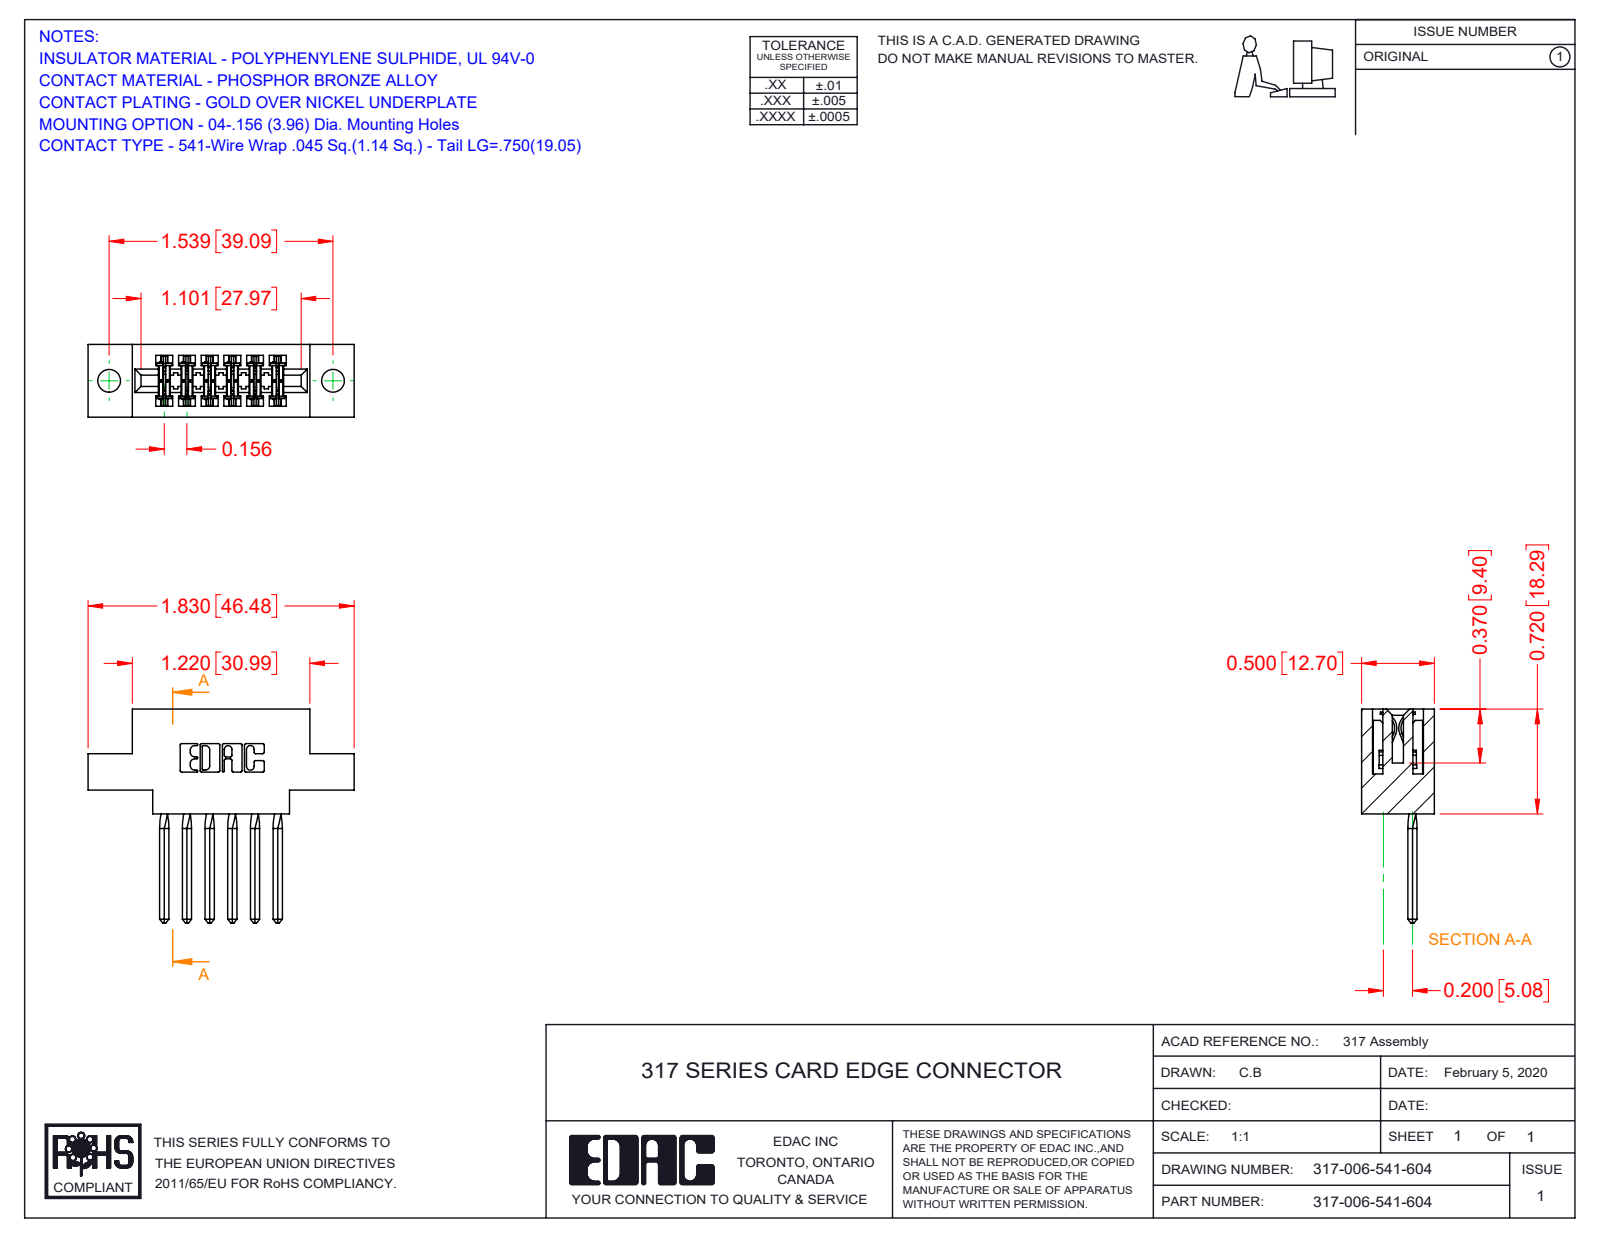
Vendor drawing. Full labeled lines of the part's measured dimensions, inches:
Part name (STEP PRODUCT): 317-006-541-604; 317-290-002_541; 317 Part_.156 Dia - TH
STEP written by: SolidWorks 2016 (CONFIG_CONTROL_DESIGN)
Units: inches
Bodies: 7 solids, 1014 faces (802 planar, 188 cylindrical, 24 other)
Overall size (bounding box): 1.83 × 1.47 × 0.5
Volume: 0.387 in³ · Surface area: 11.75 in²
Round holes (diameter × count): ⌀0.156 ×2
Partial cylindrical surfaces — rounded edges, fillets, slot ends (radius × count): R0.01 ×22, R0.015 ×12, R0.007 ×6, R0.031 ×6, R0.026 ×3, R0.095 ×2, R0.1 ×2, R0.11 ×2
Main face-to-face distances: 0.5, 0.075, 0.425, 0.11, 0.156, 0.065, 0.116, 0.163, 0.22, 0.136
Hole centre spacings: 1.539
